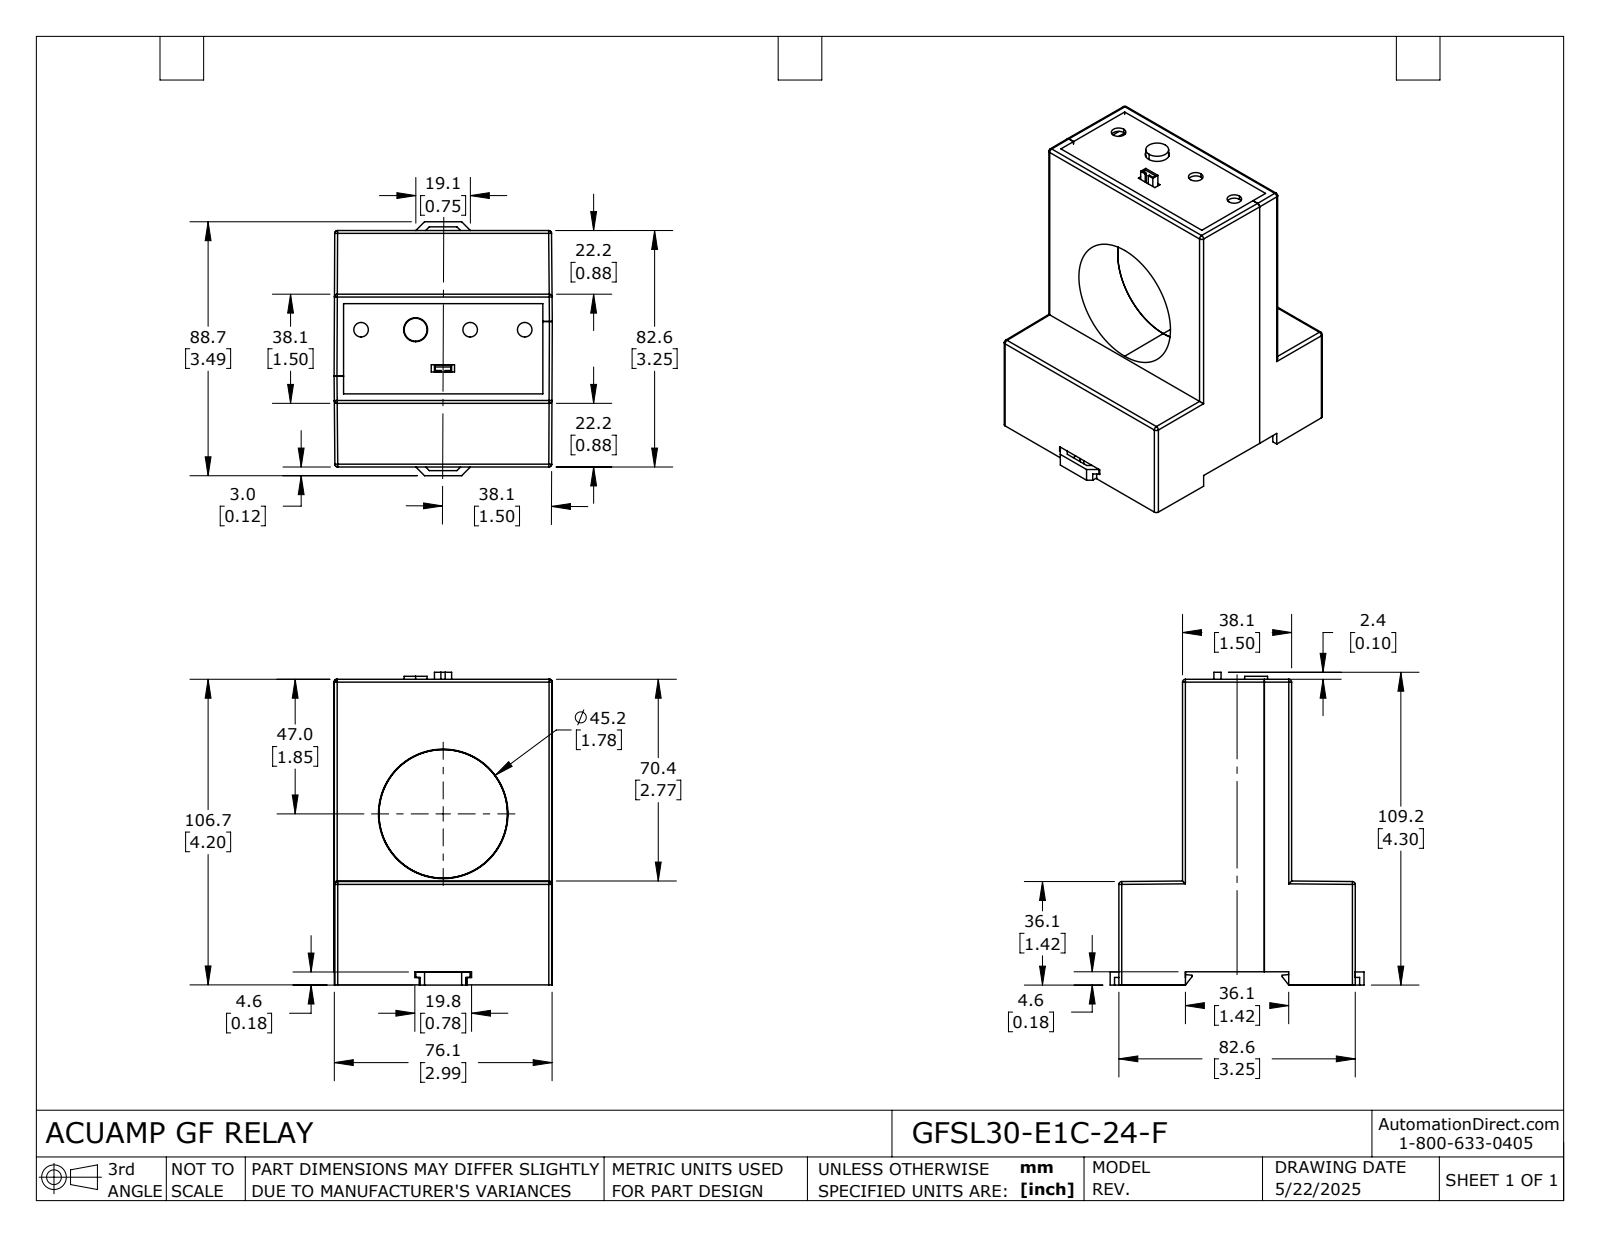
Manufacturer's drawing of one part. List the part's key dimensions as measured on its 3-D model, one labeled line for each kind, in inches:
Part name (STEP PRODUCT): GFSL30-E1C-24-F
STEP written by: SolidWorks 2024 (AUTOMOTIVE_DESIGN)
Units: inches
Bodies: 8 solids, 1046 faces (890 planar, 120 cylindrical, 36 other)
Overall size (bounding box): 4.299 × 3.49 × 3
Volume: 5.534 in³ · Surface area: 153.9 in²
Round holes (diameter × count): ⌀0.2 ×7, ⌀0.33 ×4, ⌀0.12 ×2
Round bosses / shafts (diameter × count): ⌀0.1 ×2, ⌀0.315 ×1
Partial cylindrical surfaces — rounded edges, fillets, slot ends (radius × count): R0.02 ×23, R0.039 ×20, R0.008 ×4, R0.012 ×4, R0.104 ×4, R0.18 ×4
Main face-to-face distances: 0.08, 0.875, 2.295, 1.42, 2.916, 0.08, 2.996, 1.5, 0.795, 2.215
Hole centre spacings: 0.75, 0.919, 1.5, 0.531, 1.591, 2.25, 2.312, 0.993
